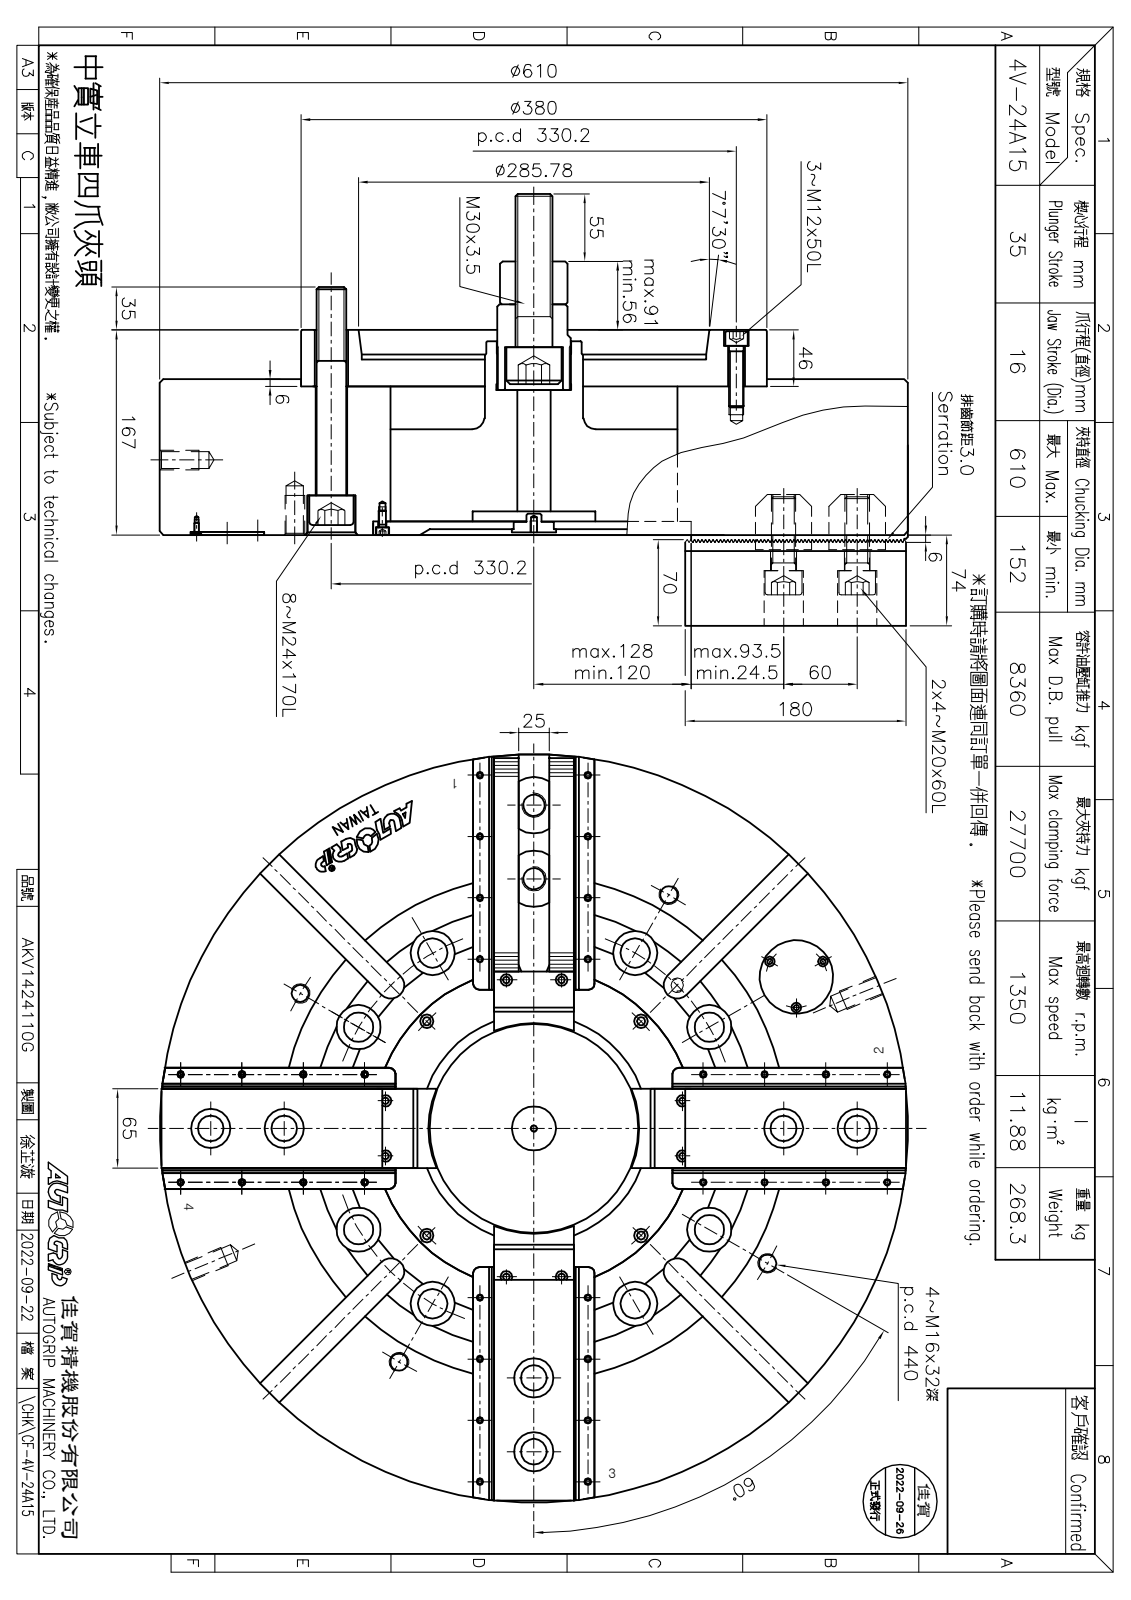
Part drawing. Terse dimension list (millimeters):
name: CF-3V-21-06000; 圓頭內六角螺栓_M6x14; CF-3V-24-03000; 圓頭內六角螺栓_M12x50 (+8 more)
written by: SolidWorks 2016 (CONFIG_CONTROL_DESIGN)
unit: mm
bodies: 91 solids, 7295 faces (5154 planar, 1545 cylindrical, 596 other)
size: 611 × 611 × 351.08
volume: 39 700 000 mm³; area: 2 754 000 mm²
holes: 32× ⌀4.2, 32× ⌀5.5, 12× ⌀26, 8× ⌀21, 8× ⌀32, 8× ⌀39, 6× ⌀14, 4× ⌀6.6, 4× ⌀11, 3× ⌀3.3, 3× ⌀4.6, 3× ⌀13
bosses: 32× ⌀9.5, 32× ⌀5, 9× ⌀36, 8× ⌀30, 8× ⌀24, 8× ⌀20, 4× ⌀12, 4× ⌀10
rounds: 460× R0.1, 4× R11, 4× R18.5, 3× R15, 2× R2.5, 1× R60, 1× R112, 1× R130
face distances: 6, 121, 127, 65, 53.5, 47.5, 73.5, 5, 45, 116
hole spacings: 50, 101.21, 88, 100, 133.21, 426, 434.99, 150
